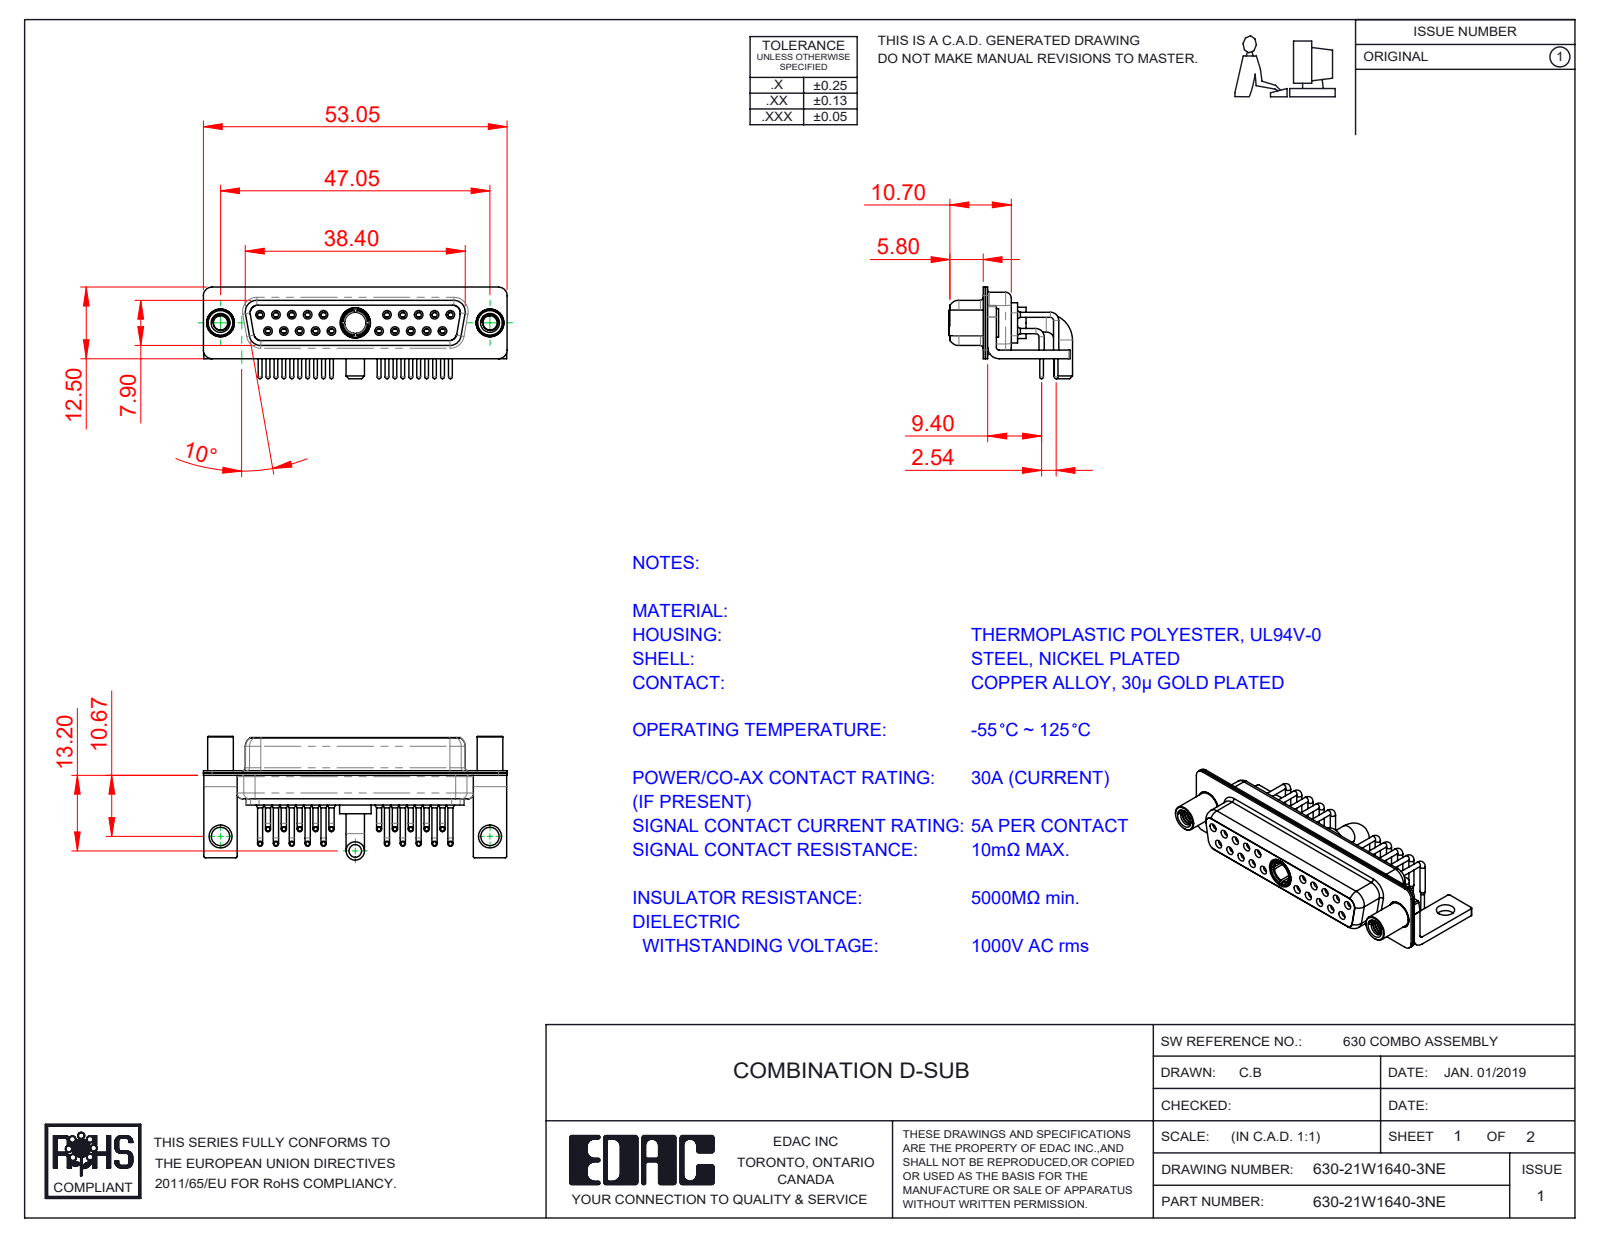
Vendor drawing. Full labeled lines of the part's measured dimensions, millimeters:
Part name (STEP PRODUCT): 630Combo Shell Rear_25 Contacts; 630-21W1640-3NE; 630Combo Housing_21W1; 630Combo Shell Front_25 Contacts (+5 more)
STEP written by: SolidWorks 2020 (CONFIG_CONTROL_DESIGN)
Units: millimetres
Bodies: 29 solids, 1515 faces (418 planar, 694 cylindrical, 403 other)
Overall size (bounding box): 53.05 × 21.6 × 16
Volume: 4 438 mm³ · Surface area: 10 293 mm²
Round holes (diameter × count): ⌀0.9 ×20, ⌀1.1 ×20, ⌀1.5 ×20, ⌀2 ×20, ⌀1.6 ×10, ⌀1.7 ×10, ⌀4.85 ×3, ⌀2.5 ×2, ⌀3.2 ×2, ⌀4 ×2, ⌀4.05 ×2, ⌀3.7 ×1
Round bosses / shafts (diameter × count): ⌀0.9 ×20, ⌀0.65 ×20, ⌀1.6 ×10, ⌀5 ×2, ⌀4.95 ×2, ⌀4.8 ×2, ⌀4.5 ×2, ⌀3.2 ×2
Partial cylindrical surfaces — rounded edges, fillets, slot ends (radius × count): R0.25 ×16, R1.5 ×16, R2 ×13, R1.35 ×8, R1.6 ×8, R0.5 ×5, R0.6 ×4, R0.65 ×4
Main face-to-face distances: 0.4, 0.45, 1.4, 8.45, 0.8, 1.8, 8.9, 6.2, 7.05, 1.5
Hole centre spacings: 3.16, 2.77, 5.54, 8.31, 5.04, 19.39, 20.97, 22.16
